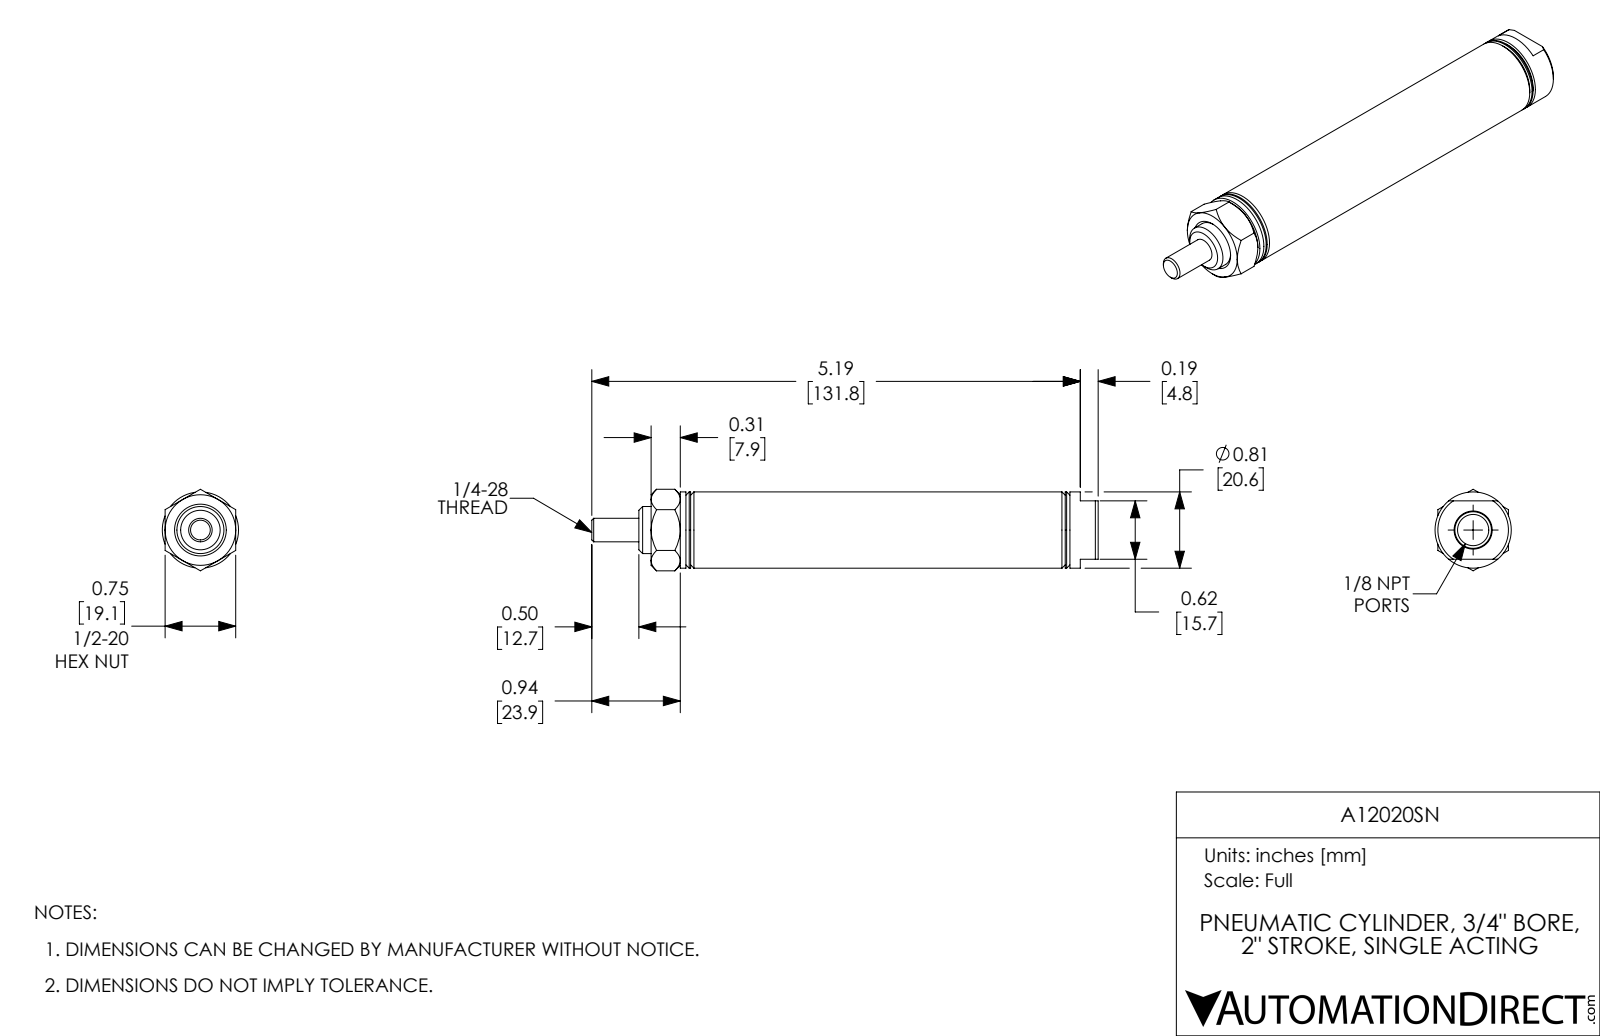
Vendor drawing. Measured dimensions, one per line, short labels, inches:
name: A12020SN; A12020SN_Mounting Nut_D-98; A12020SN-Rod; A12020SN-MainBody
written by: SolidWorks 2017 (AUTOMOTIVE_DESIGN)
unit: in
bodies: 3 solids, 82 faces (25 planar, 24 cylindrical, 33 other)
size: 5.38 × 0.866 × 0.81
volume: 1.586 in³; area: 28.96 in²
holes: 1× ⌀0.25, 1× ⌀0.332, 1× ⌀0.5, 1× ⌀0.75
bosses: 1× ⌀0.81
face distances: 3.47, 0.5, 2.97, 2.5, 2, 0.97, 0.97, 1.47, 3.47, 4.44
